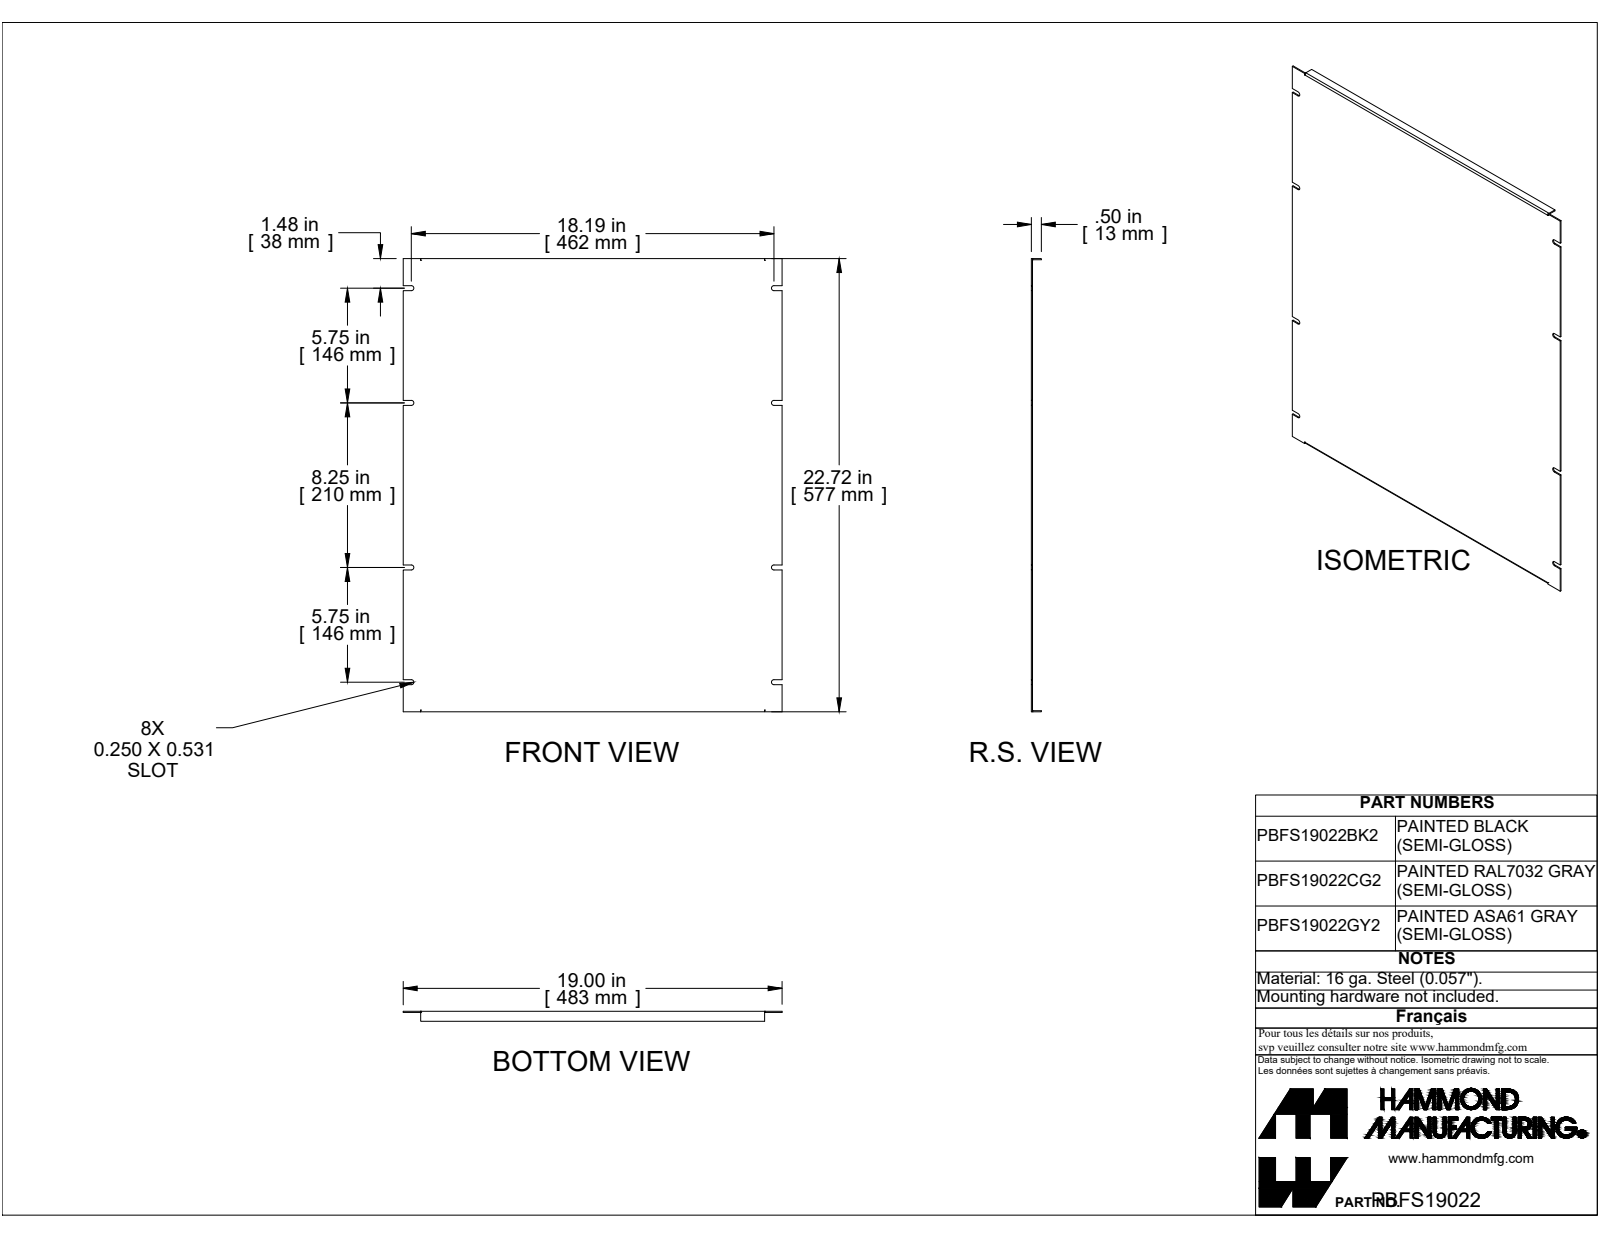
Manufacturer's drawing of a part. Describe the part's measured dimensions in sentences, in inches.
The part is named "PBFS19022". Its 3-D file was written by "SolidWorks 2019 (CONFIG_CONTROL_DESIGN)". It is 1 solid with 62 faces: 50 planar, 12 cylindrical and 0 other. Overall it measures 22.718 by 19 by 0.5 inches. Its volume is 25.37 cubic inches and its surface area 895.5 square inches. Partial cylindrical surfaces (rounded edges, fillets, slot ends): 8 of radius 0.125, 2 of radius 0.029, 2 of radius 0.086. The main face-to-face distances are 0.057, 22.661, 22.718, 22.604, 0.5, 0.443, 19, 0.25, 5.75, 14.
